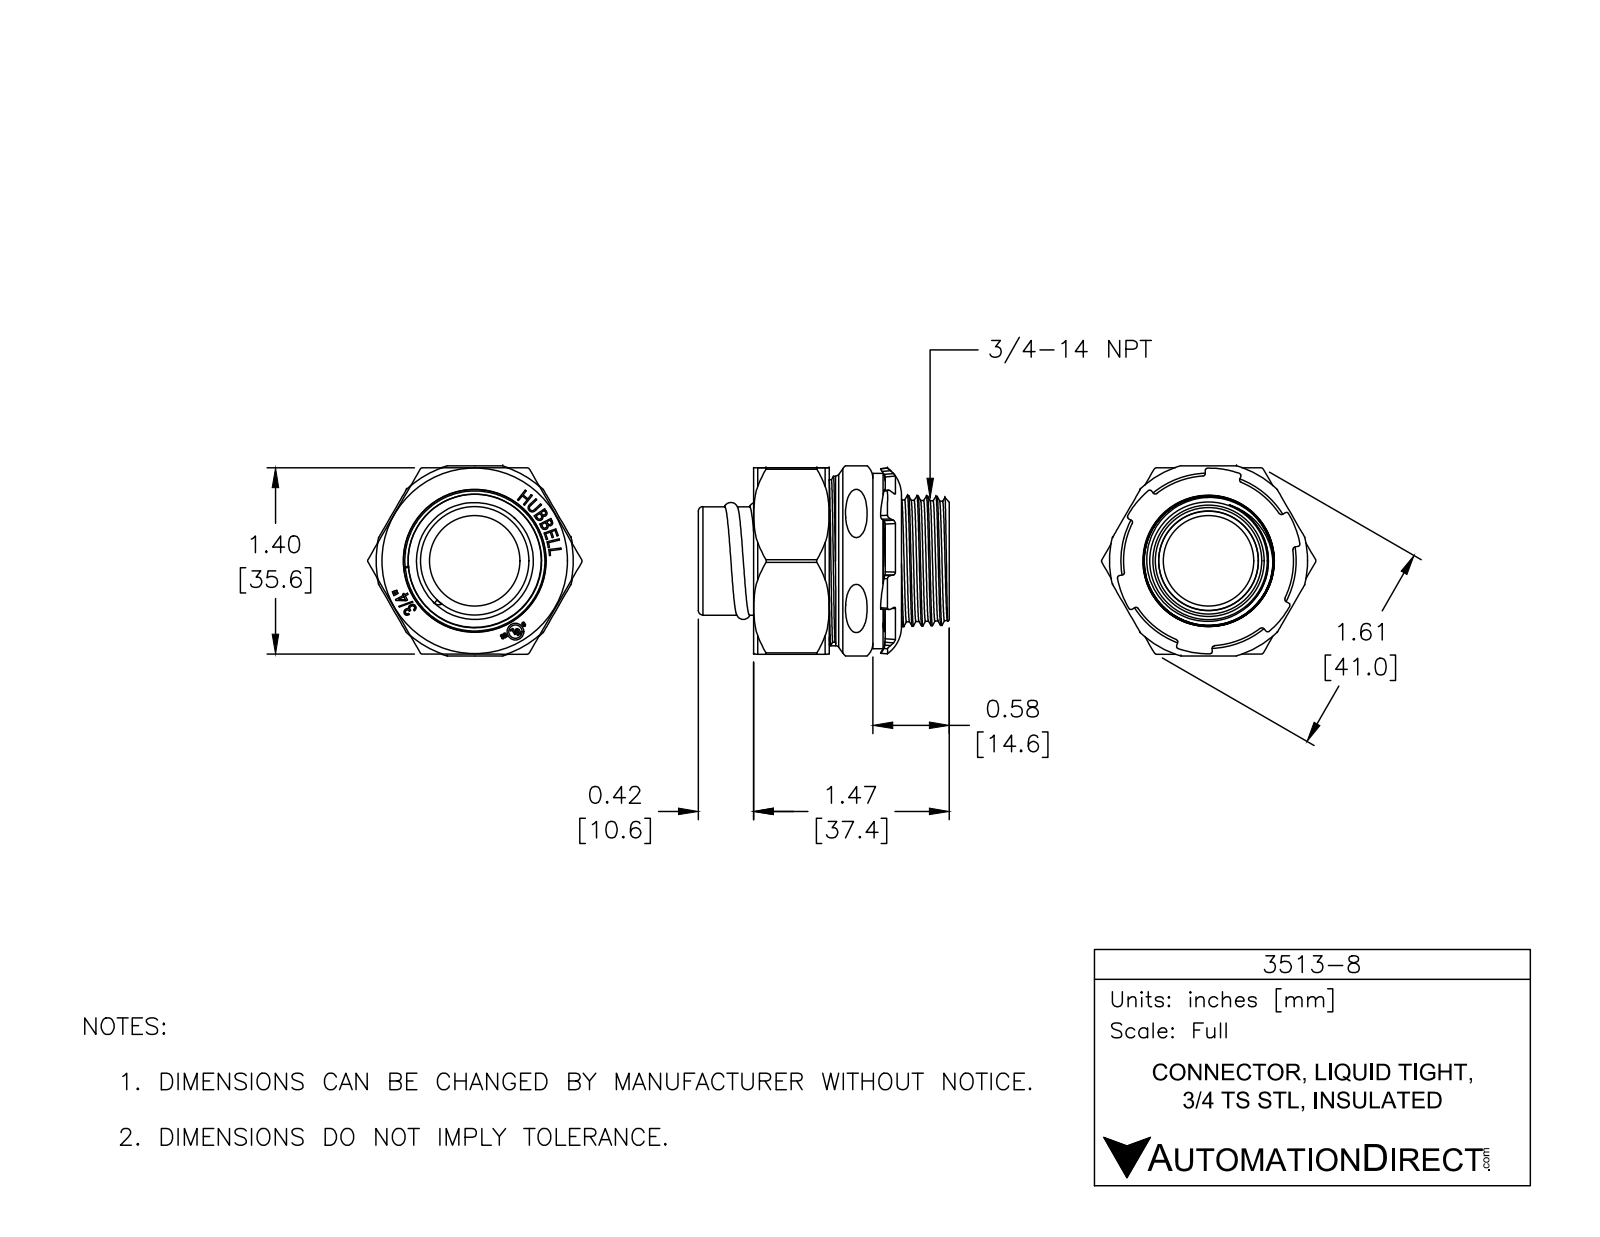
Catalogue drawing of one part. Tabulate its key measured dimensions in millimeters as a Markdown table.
| quantity | value |
| --- | --- |
| part name | 3403 SEAL; 3513RAC INSULATION BUSHING_INSTALLED; 3403 GLAND RING; 3403 FERRULE_installed (+4 more) |
| STEP written by | SolidWorks 2014 (AUTOMOTIVE_DESIGN) |
| units | millimeters |
| bodies | 7 solids, 534 faces (210 planar, 99 cylindrical, 225 other) |
| overall size | 49.5 × 41 × 37.8 |
| volume | 15 200 mm³ |
| surface area | 23 790 mm² |
| round holes (diameter × count) | 3.2 × 1, 17.3 × 1, 19.1 × 1, 23 × 1, 26.3 × 1, 27.1 × 1, 27.3 × 1, 28.3 × 1, 31.9 × 1, 33.3 × 1 |
| round bosses / shafts (diameter × count) | 33.5 × 1, 32.4 × 1, 30.8 × 1, 28 × 1, 23.2 × 1, 20.7 × 1, 19 × 1, 2.6 × 1 |
| partial cylindrical surfaces (radius × count) | 0.2 × 8, 0.5 × 6, 0.1 × 1, 0.3 × 1, 0.4 × 1, 0.8 × 1, 1.2 × 1 |
| main face-to-face distances | 35.6, 22.8, 24.7, 2, 35.6, 4, 20.8, 2, 37.4, 16.6 |
| hole center spacings | 15.6 |
